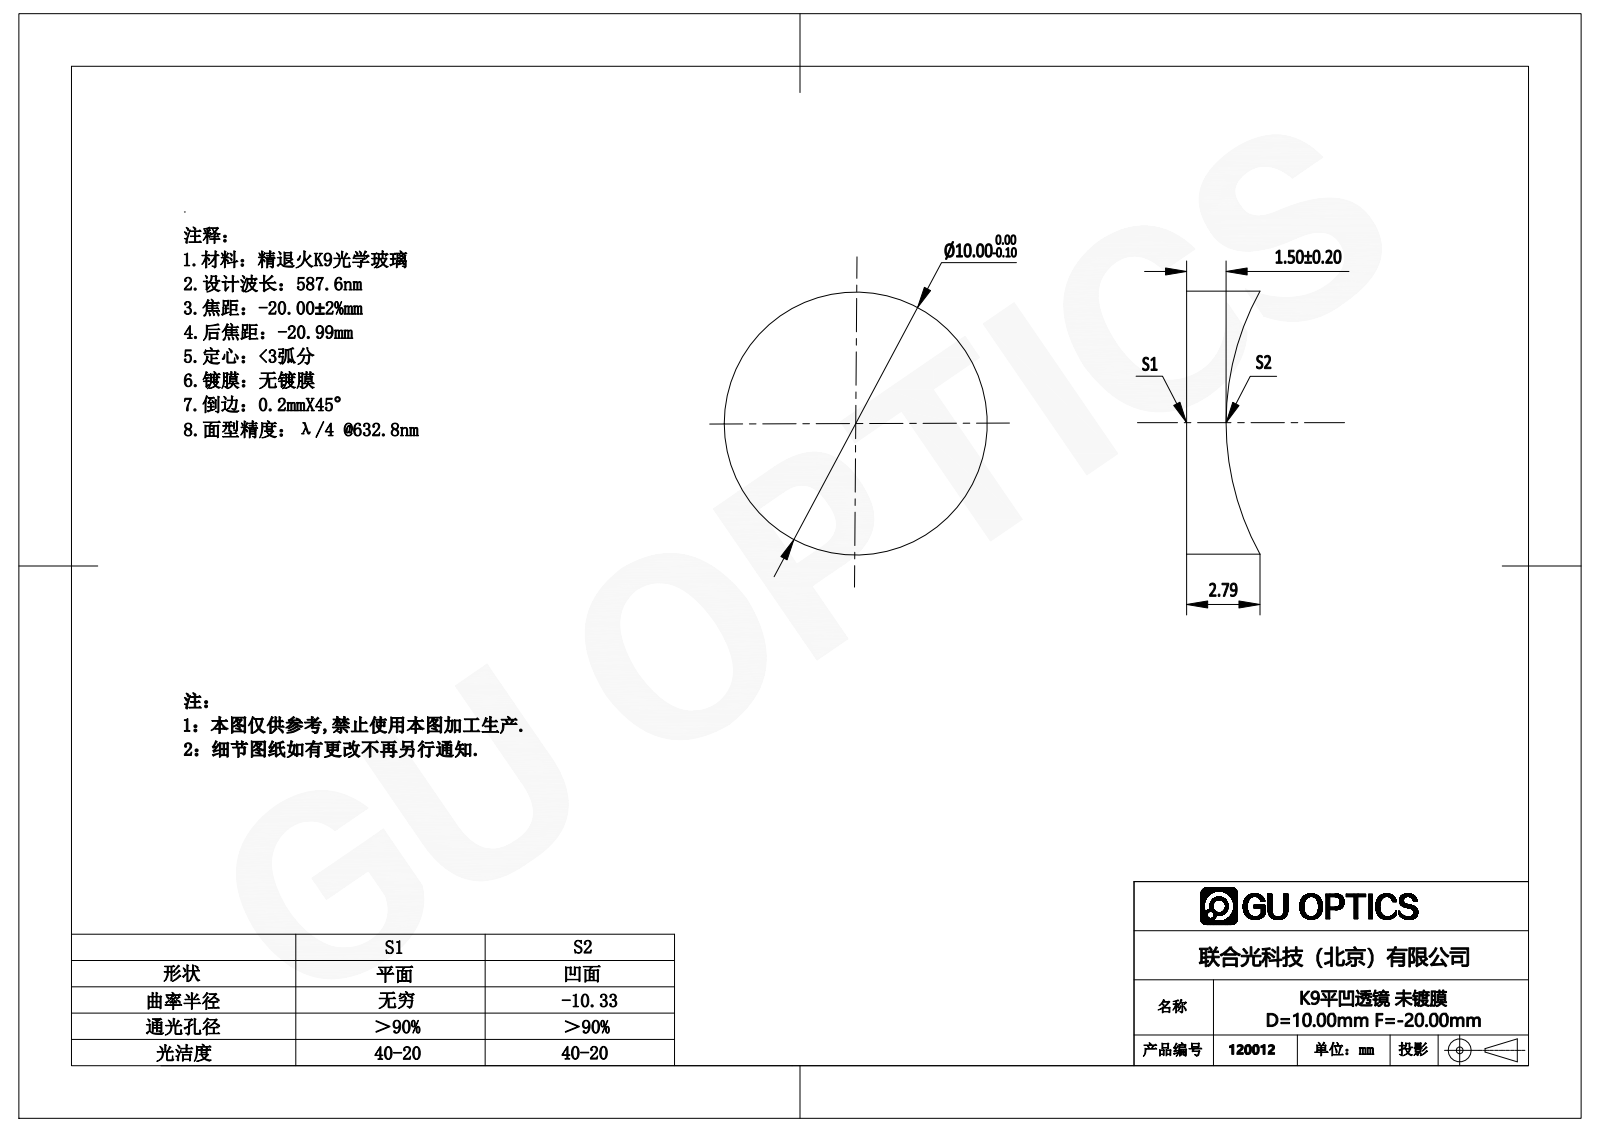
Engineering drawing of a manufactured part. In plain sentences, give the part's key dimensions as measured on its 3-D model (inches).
The part is named "120012". Its 3-D file was written by "SolidWorks 2016 (AUTOMOTIVE_DESIGN)". It is 1 solid with 5 faces: 1 planar, 2 cylindrical and 2 other. Overall it measures 0.394 by 0.394 by 0.11 inches. Its volume is 0.01 cubic inches and its surface area 0.388 square inches. Round bosses or shafts: 1 of diameter 0.394.
